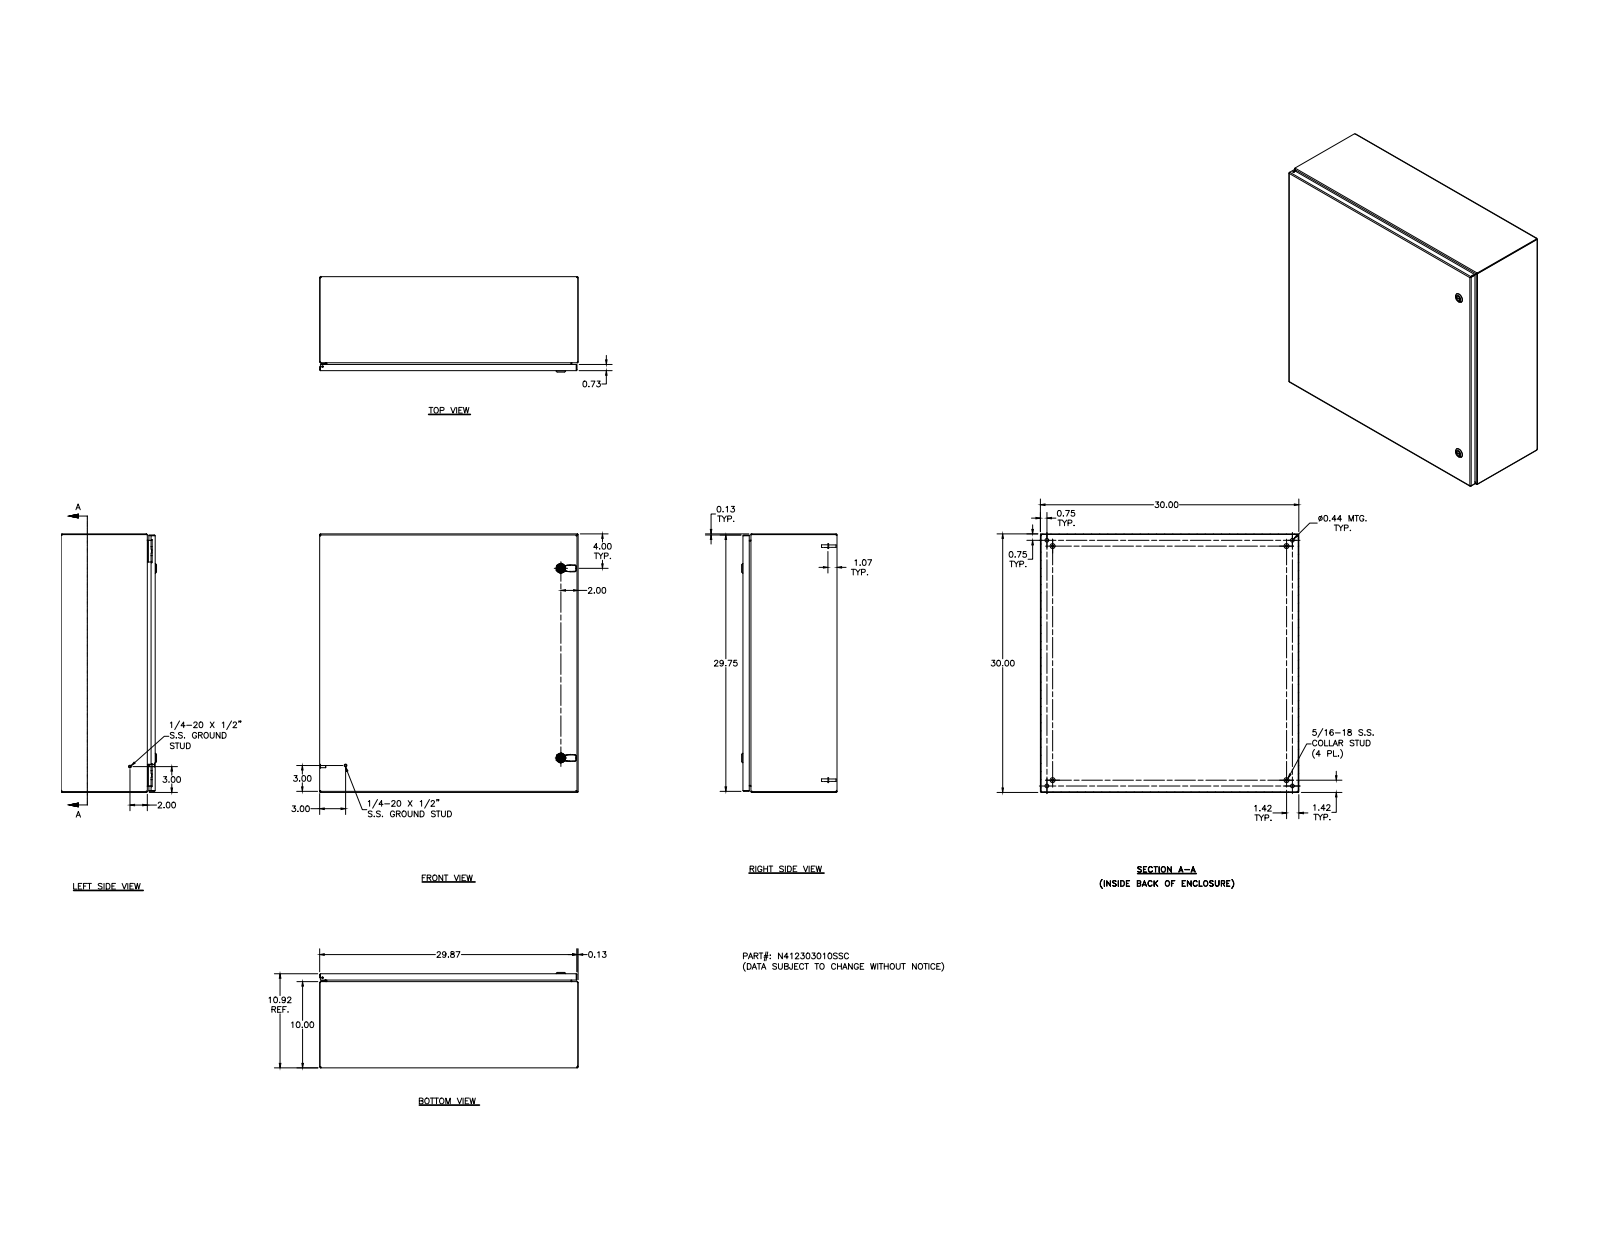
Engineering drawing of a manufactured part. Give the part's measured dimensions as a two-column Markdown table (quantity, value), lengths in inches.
| quantity | value |
| --- | --- |
| part name | N412303010SSC; N412303010SSCBKP; 388151; N4123030SSCLID (+8 more) |
| STEP written by | Autodesk Inventor 2011 (AUTOMOTIVE_DESIGN) |
| units | inches |
| bodies | 42 solids, 1682 faces (706 planar, 600 cylindrical, 376 other) |
| overall size | 30 × 30 × 11.075 |
| volume | 240 in³ |
| surface area | 6 507 in² |
| round holes (diameter × count) | 0.188 × 5, 0.093 × 4, 0.152 × 4, 0.167 × 4, 0.172 × 4, 0.437 × 4, 0.156 × 2, 0.197 × 2, 0.315 × 2, 0.394 × 2, 0.402 × 2, 0.634 × 2 |
| round bosses / shafts (diameter × count) | 0.25 × 10, 0.563 × 4, 0.36 × 4, 0.32 × 4, 0.3 × 4, 0.275 × 4, 0.256 × 4, 0.164 × 4 |
| partial cylindrical surfaces (radius × count) | 0.031 × 30, 0.05 × 26, 0.105 × 20, 0.016 × 18, 0.02 × 15, 0.125 × 14, 0.032 × 8, 0.07 × 8 |
| main face-to-face distances | 0.074, 10.843, 29.926, 10.917, 10.769, 29.852, 30, 9.926, 0.917, 0.739 |
| hole center spacings | 26, 0.017, 0.66, 28.5, 27.698, 0.019, 0.5, 0.648 |
